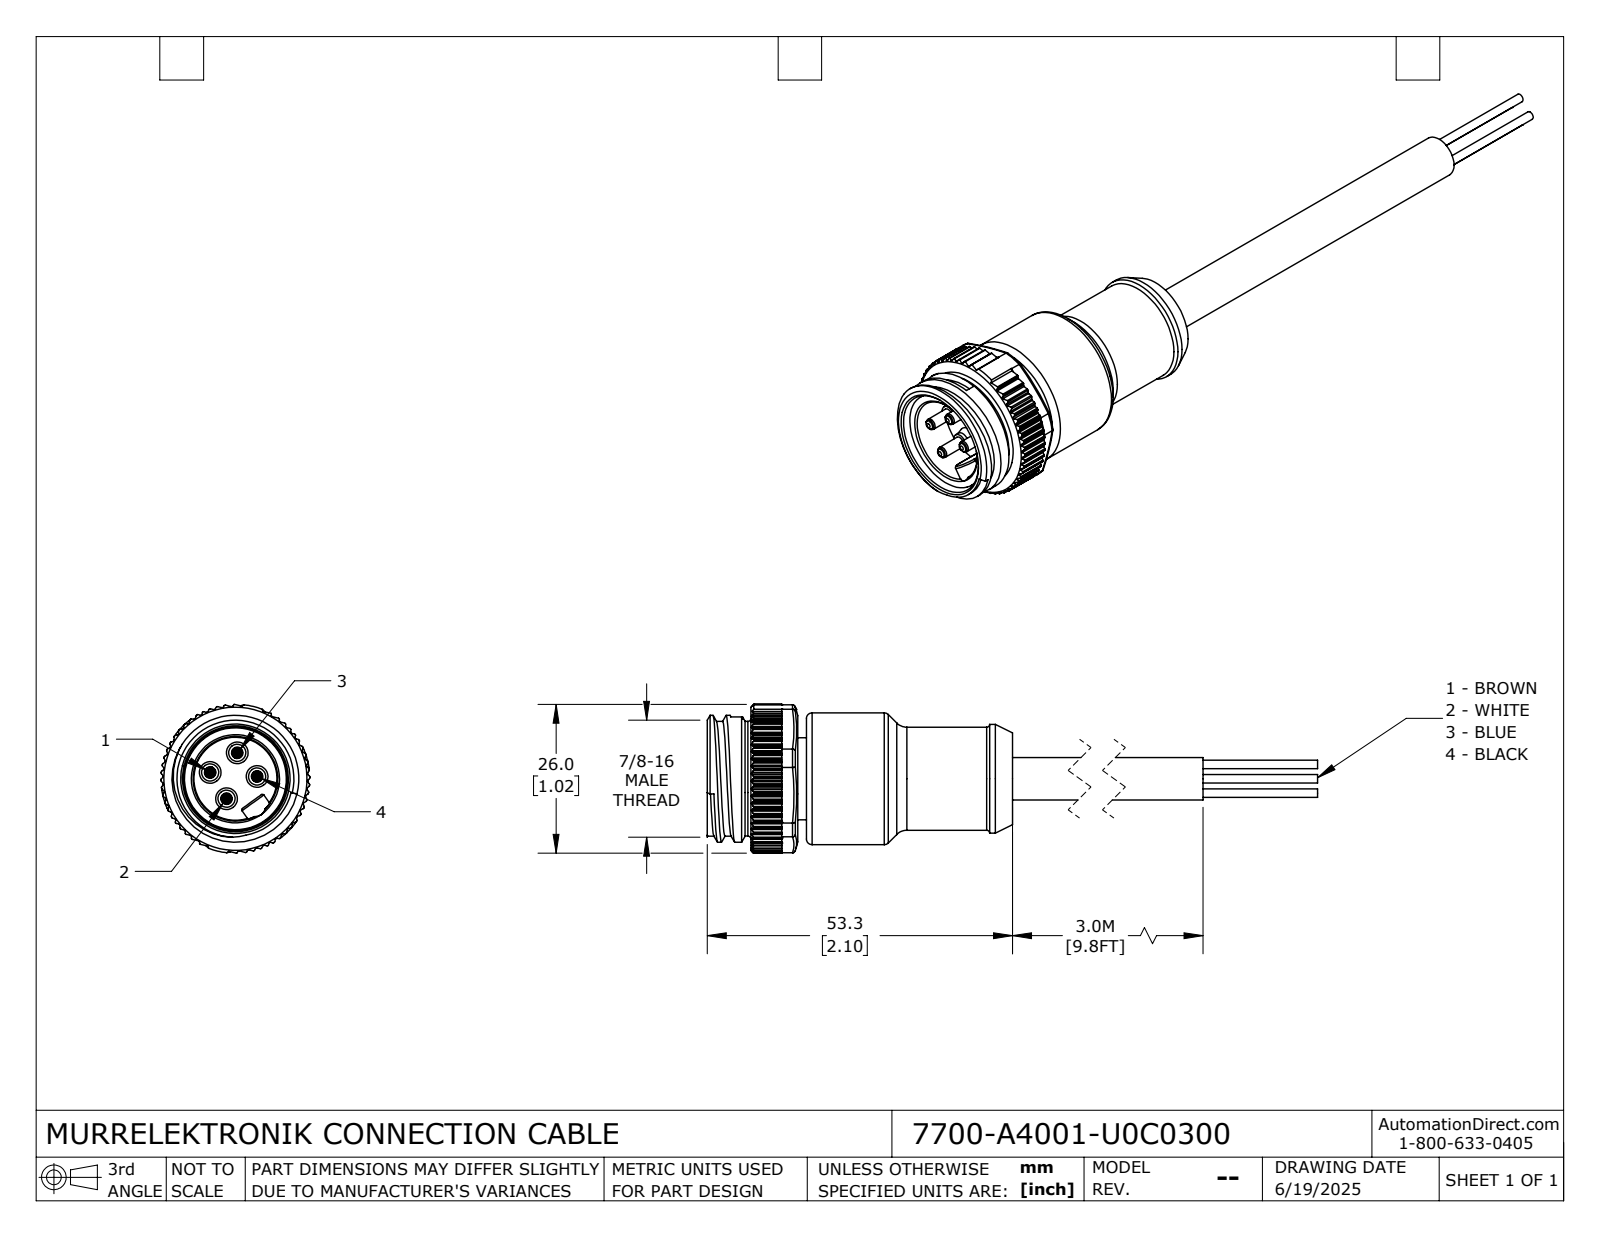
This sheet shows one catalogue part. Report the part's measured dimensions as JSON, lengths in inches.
{"part_name": "7700-A4001-U0C0300", "step_written_by": "SolidWorks 2024 (CONFIG_CONTROL_DESIGN)", "units": "inches", "bodies": {"solids": 1, "faces": 580, "planar": 236, "cylindrical": 266, "other": 78}, "overall_size": [5.642, 1.024, 1.024], "volume_in3": 1.227, "surface_area_in2": 14.39, "round_holes": [[0.614, 1], [0.728, 1]], "round_bosses_or_shafts": [[0.118, 4], [0.079, 4], [0.059, 4], [0.906, 1], [0.873, 1], [0.789, 1], [0.787, 1], [0.748, 1]], "partial_cylinders_radius": [[0.008, 126], [0.012, 18], [0.004, 4], [0.028, 4], [0.093, 1], [0.512, 1]], "face_to_face_distances": [0.059, 1.476, 1.417, 0.323, 0.382, 1.799, 0.035, 0.287, 0.346, 1.764]}
